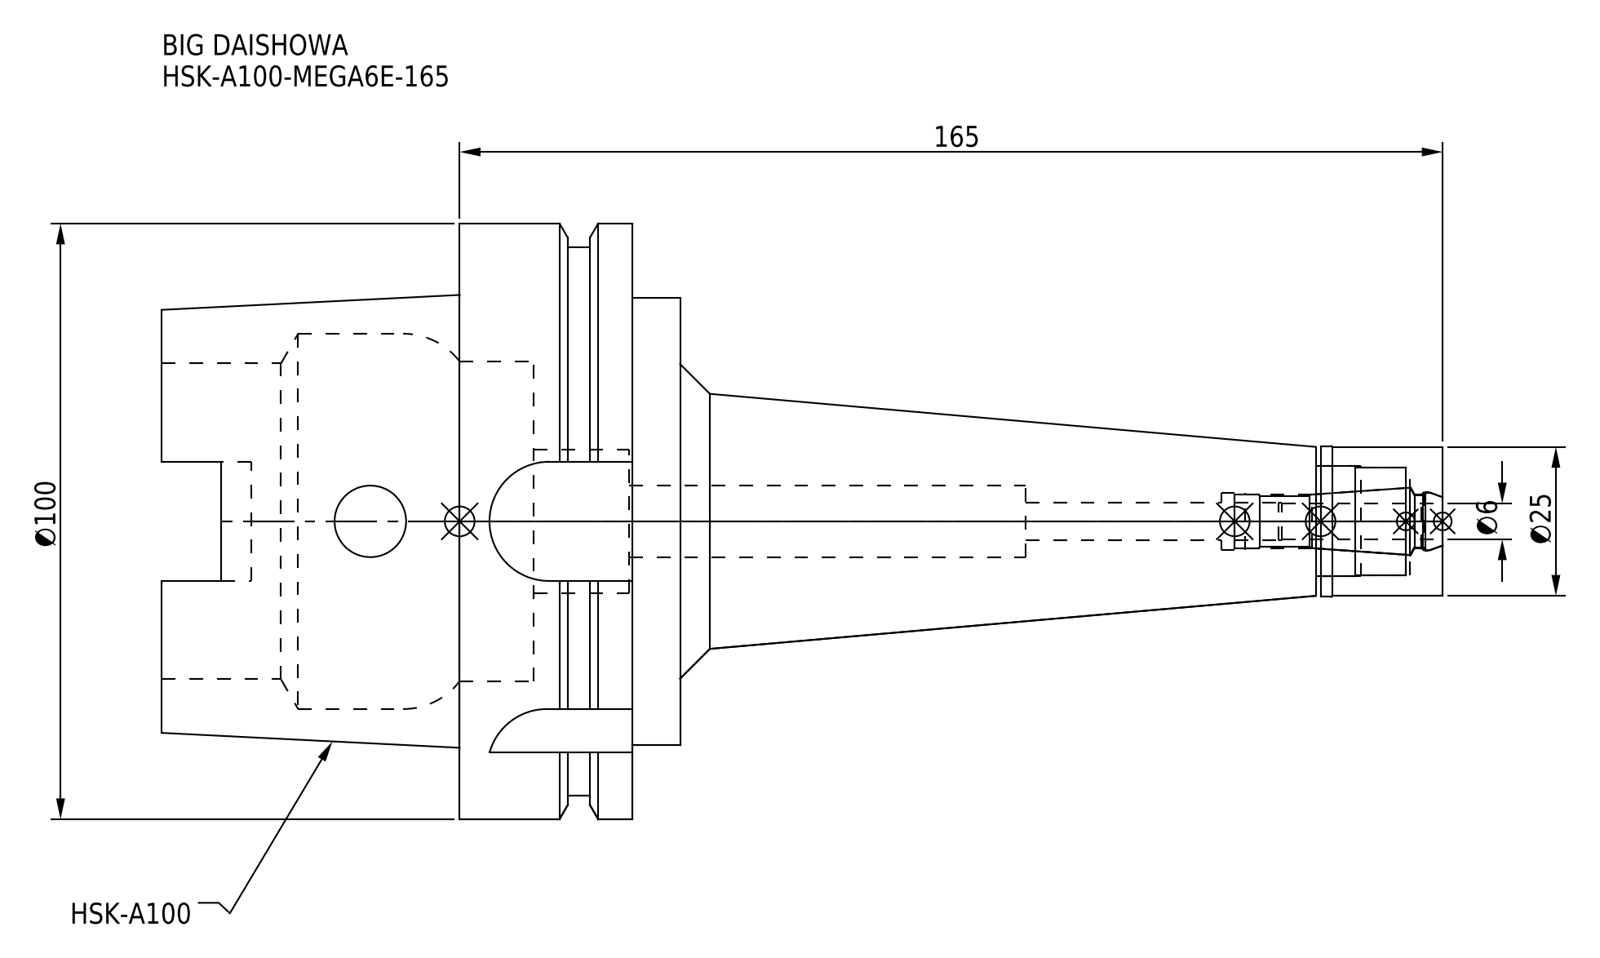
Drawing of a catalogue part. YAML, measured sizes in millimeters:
part_name: "HSK-A100-MEGA6E-165-060-FreeParts; MEN6_1.stp; HSK-A100-MEGA6E-165-060.stp; HSK-A100-MEGA6E-165 (+3 more)"
step_written_by: "SolidWorks 2019 (CONFIG_CONTROL_DESIGN)"
units: millimeters
bodies: {solids: 2, faces: 126, planar: 42, cylindrical: 56, other: 28}
overall_size: [215, 100, 100]
volume: 390727
surface_area: 70516
round_holes:
  - {diameter: 12, count: 2}
  - {diameter: 6.4, count: 1}
  - {diameter: 9, count: 1}
  - {diameter: 9.6, count: 1}
  - {diameter: 9.9, count: 1}
  - {diameter: 18, count: 1}
  - {diameter: 18.5, count: 1}
  - {diameter: 24, count: 1}
  - {diameter: 53, count: 1}
  - {diameter: 53.8, count: 1}
  - {diameter: 63, count: 1}
round_bosses_or_shafts:
  - {diameter: 100, count: 1}
  - {diameter: 92, count: 1}
  - {diameter: 75, count: 1}
  - {diameter: 25.3, count: 1}
  - {diameter: 25, count: 1}
partial_cylinders:
  - {radius: 4.88, count: 4}
  - {radius: 10, count: 4}
face_to_face_distances: [29, 8, 37, 24.55, 16.55, 12.45, 87, 79, 62.45, 50]
